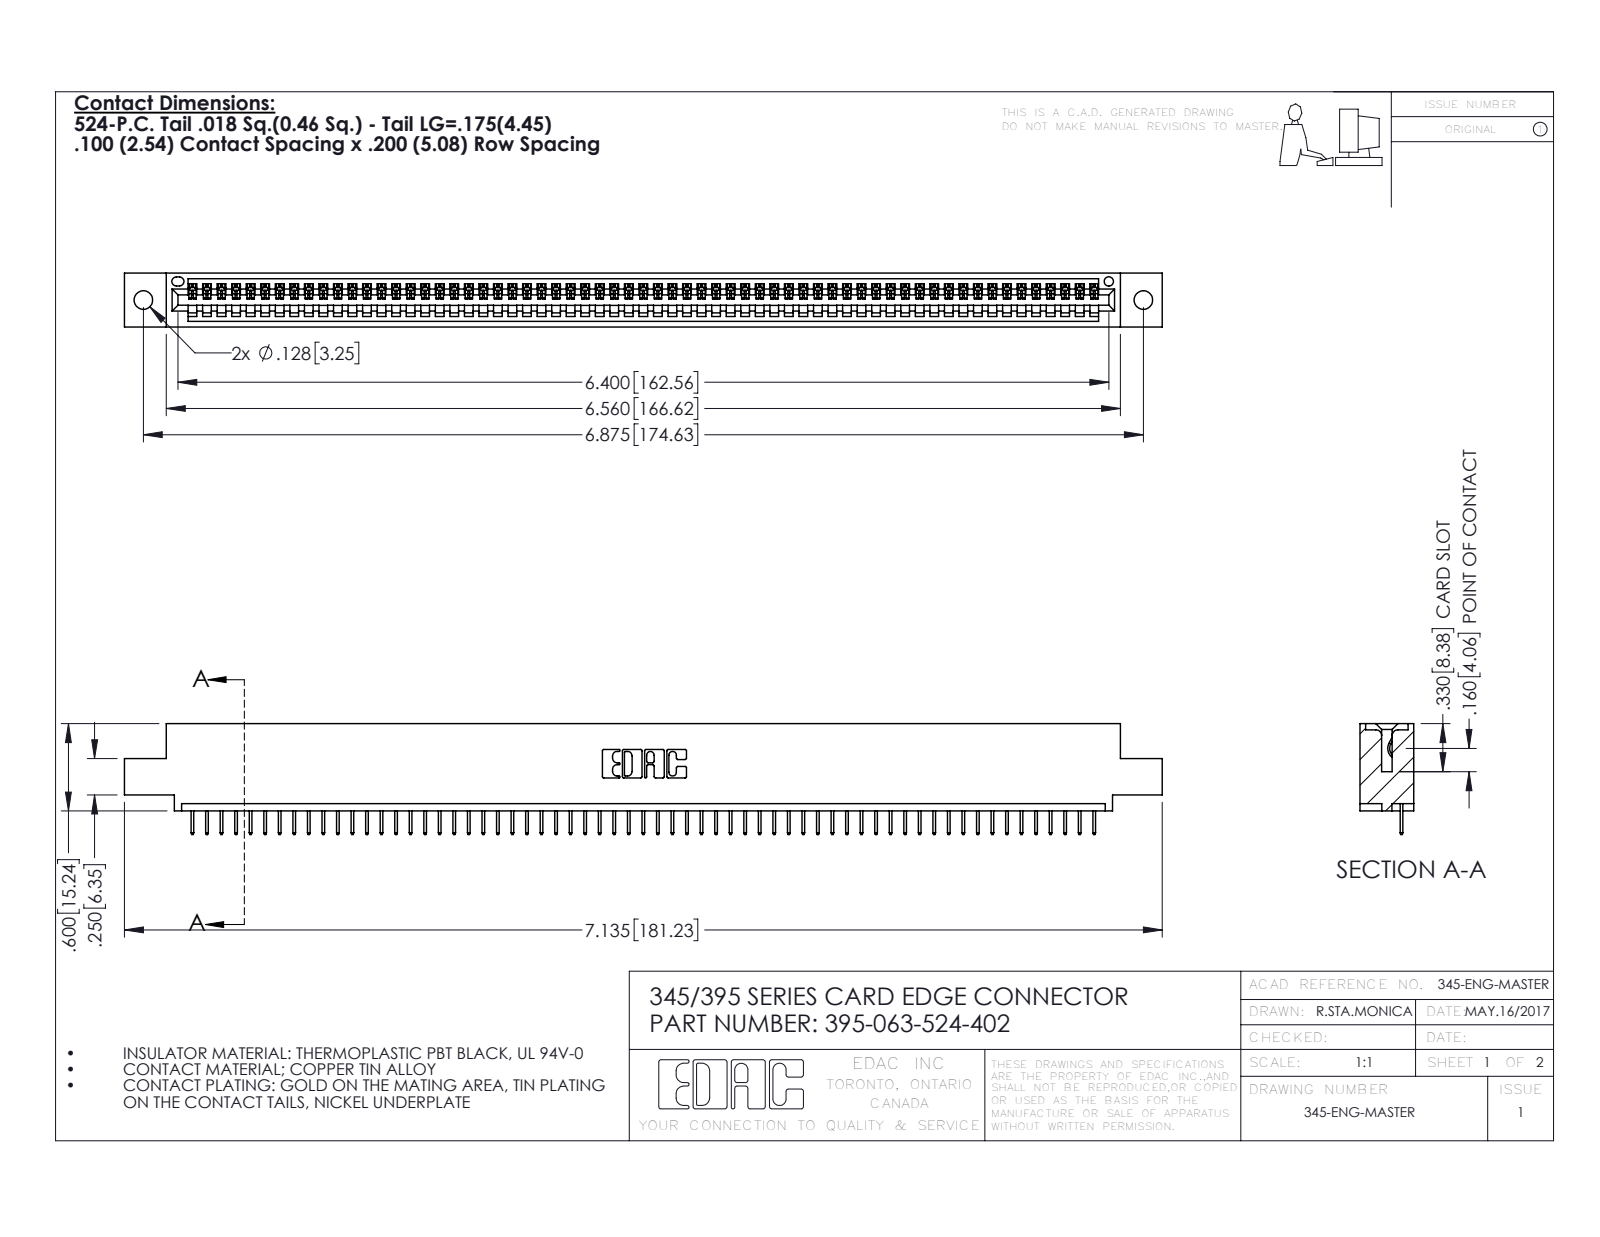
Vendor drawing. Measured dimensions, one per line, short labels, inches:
name: 345-292-001_345-293-124; 395-063-524-402; 345 Part_0.110 Offset - 0.128 Dia
written by: SolidWorks 2016 (CONFIG_CONTROL_DESIGN)
unit: in
bodies: 64 solids, 4036 faces (2982 planar, 1054 cylindrical, 0 other)
size: 7.135 × 0.762 × 0.37
volume: 1.039 in³; area: 33.99 in²
holes: 2× ⌀0.128, 1× ⌀0.064
rounds: 126× R0.006, 22× R0.01, 6× R0.007, 6× R0.031, 3× R0.026, 2× R0.031, 2× R0.04, 1× R0.014
face distances: 0.072, 0.298, 0.37, 0.2, 0.098, 0.272, 0.025, 0.225, 0.072, 0.149
hole spacings: 0.27, 6.639, 6.875
